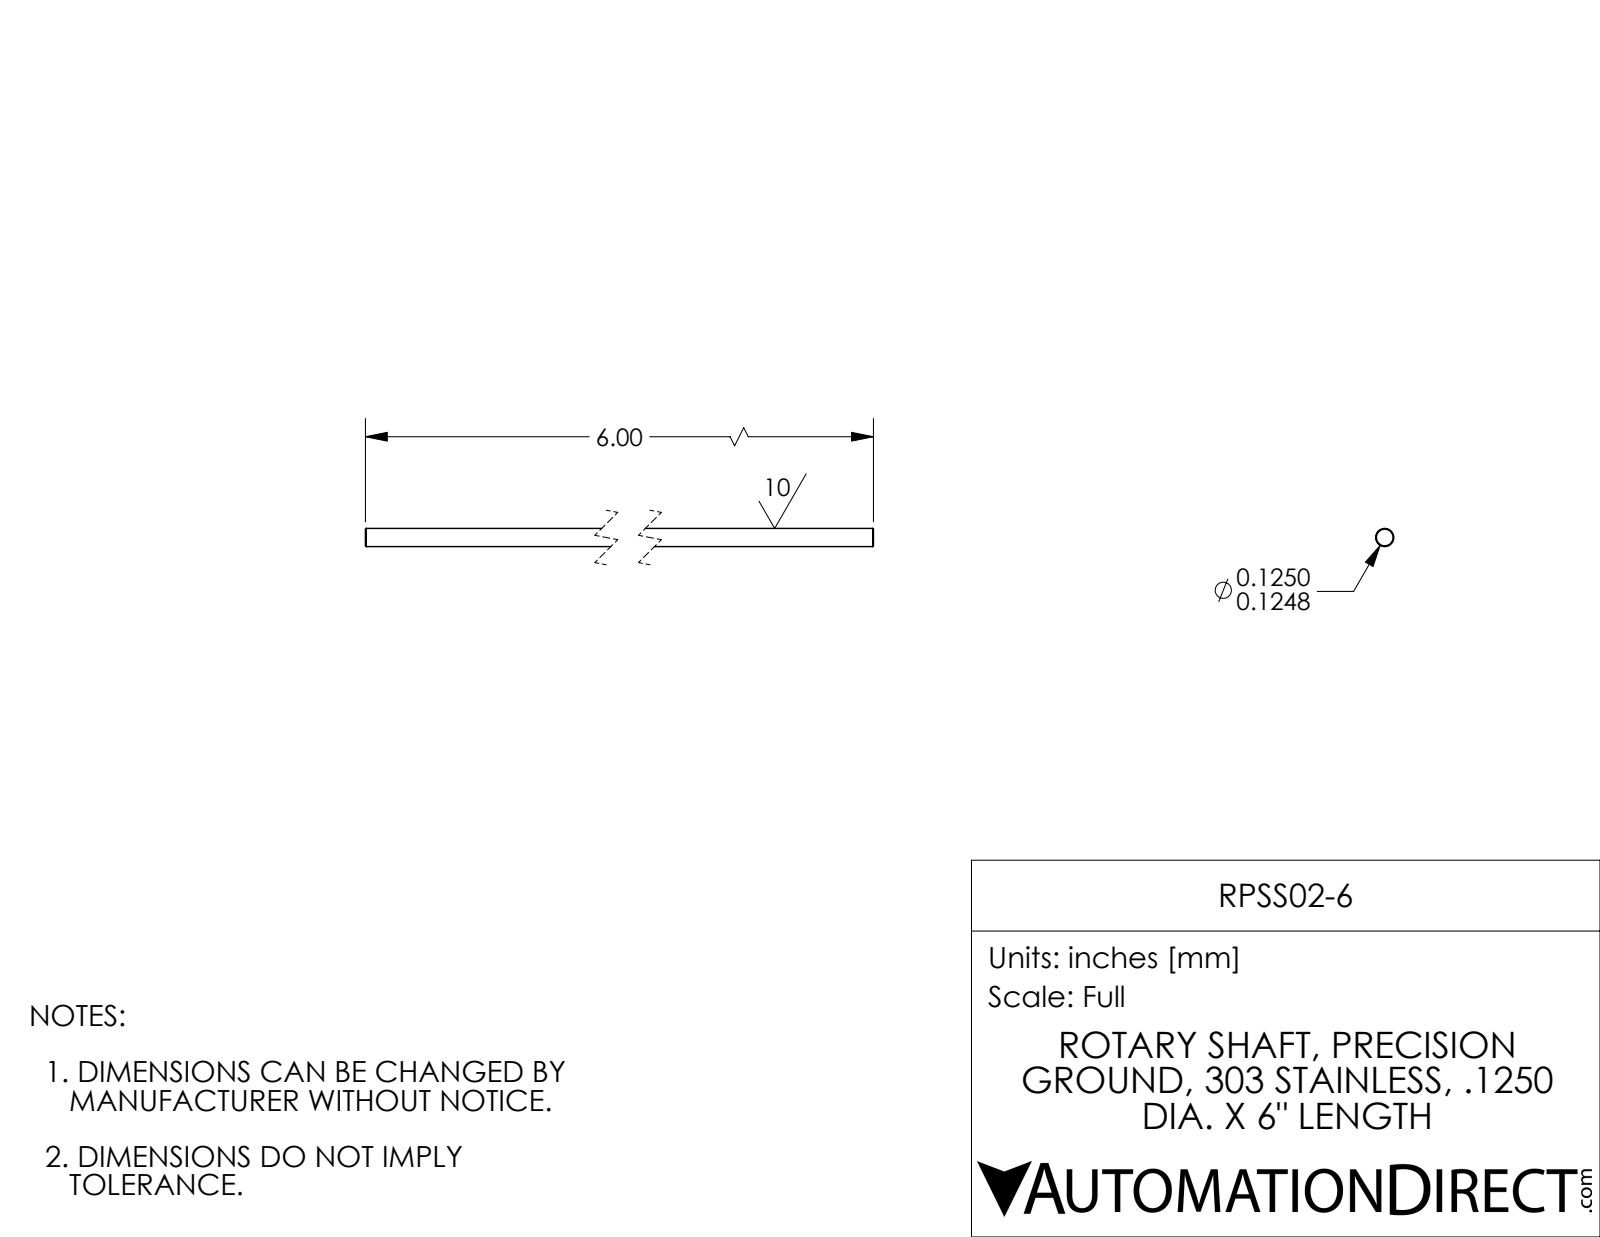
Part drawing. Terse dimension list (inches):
name: RPSS02-6
written by: SolidWorks 2017 (AUTOMOTIVE_DESIGN)
unit: in
bodies: 1 solid, 8 faces (2 planar, 2 cylindrical, 4 other)
size: 6 × 0.125 × 0.125
volume: 0.074 in³; area: 2.378 in²
bosses: 1× ⌀0.125
face distances: 6
